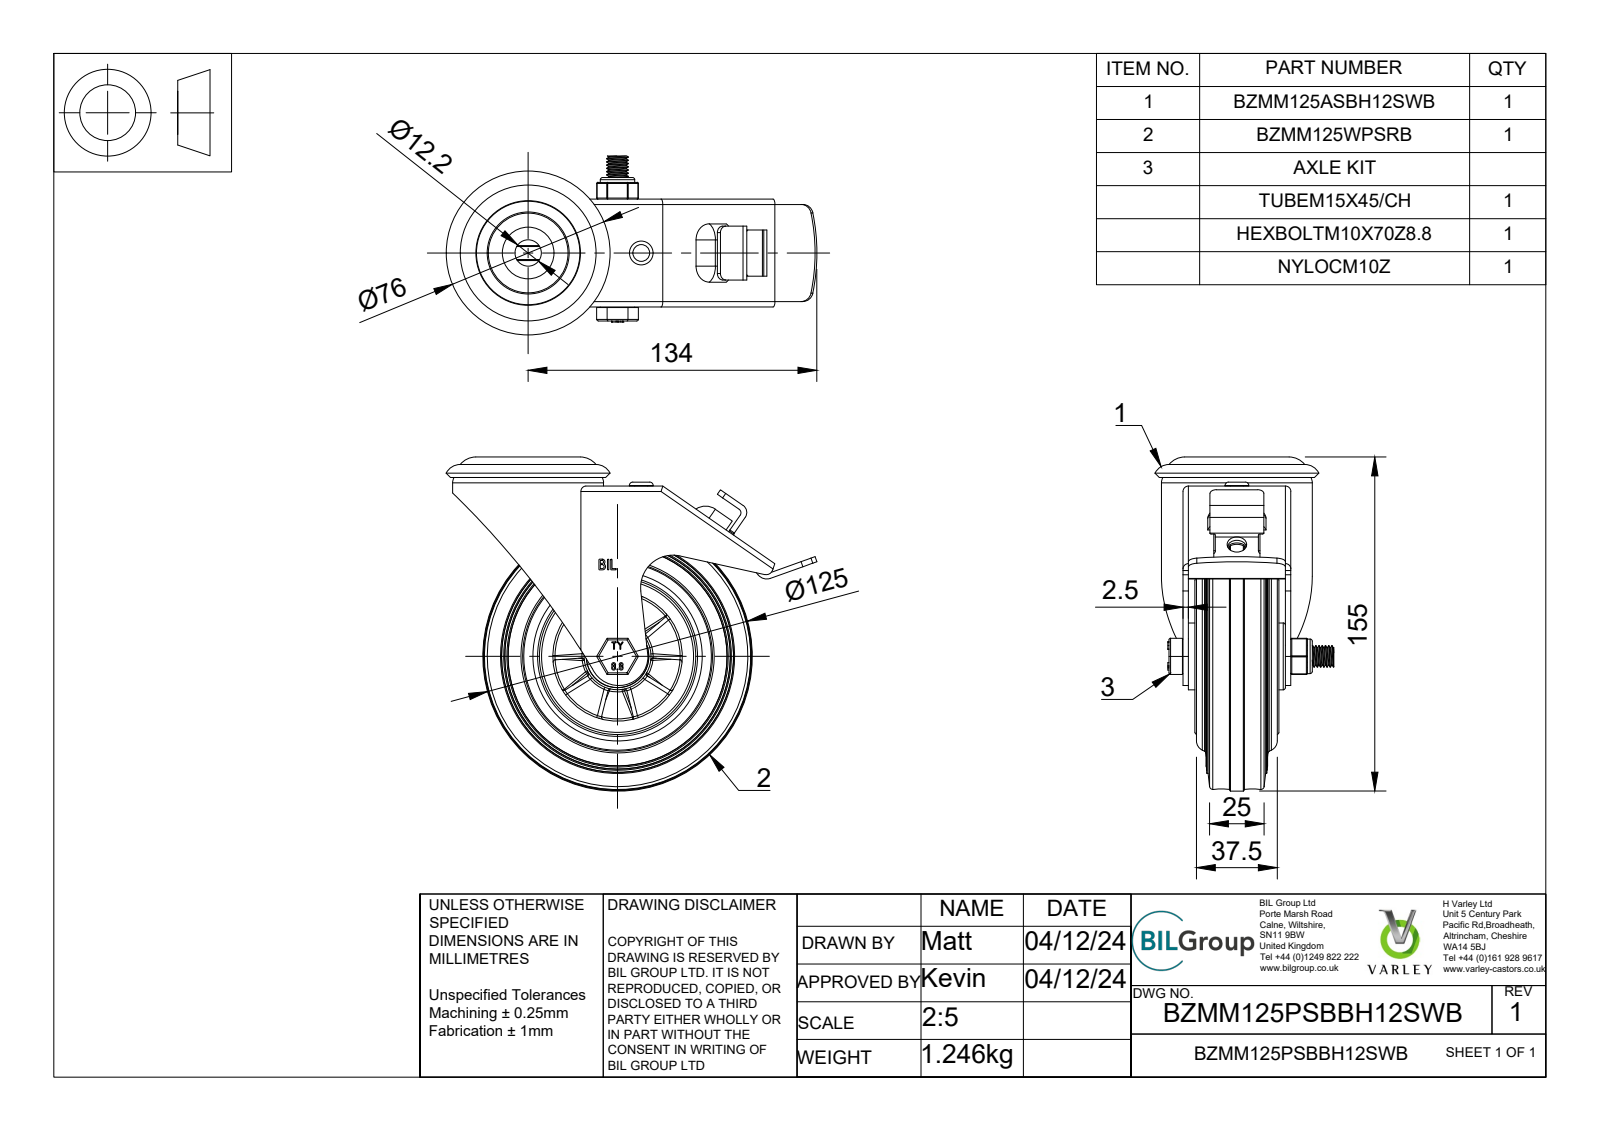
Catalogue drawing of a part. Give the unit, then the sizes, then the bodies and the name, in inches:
Units: inches
Overall size (bounding box): 6.772 × 6.102 × 3.268
Round holes (diameter × count): ⌀0.236 ×2, ⌀0.354 ×1, ⌀0.394 ×1, ⌀0.402 ×1, ⌀0.472 ×1, ⌀0.48 ×1, ⌀0.591 ×1, ⌀0.598 ×1, ⌀0.896 ×1, ⌀1.142 ×1, ⌀2.362 ×1, ⌀2.559 ×1
Round bosses / shafts (diameter × count): ⌀0.157 ×8, ⌀4.921 ×1, ⌀2.756 ×1, ⌀1.949 ×1, ⌀1.496 ×1, ⌀1.22 ×1, ⌀1.138 ×1, ⌀0.945 ×1
Partial cylindrical surfaces — rounded edges, fillets, slot ends (radius × count): R0.03 ×54, R0.02 ×32, R0.049 ×6, R0.118 ×6, R0.157 ×6, R0.098 ×5, R0.079 ×3, R0.197 ×3
Main face-to-face distances: 0.098, 1.87, 1.772, 0.256, 1.969, 0.197, 0.118, 0.039, 0.079, 0.217
Hole centre spacings: 2.067
Volume: 25.4 in³ · Surface area: 257.7 in²
Bodies: 22 solids, 1024 faces (384 planar, 243 cylindrical, 397 other)
Part name (STEP PRODUCT): BZMM125PSBBH12SWB v3; BZMM125ASBH12SWB v1; ZINC PLATED, PRESSED STEEL HEAD; ZINC PLATED, PRESSED STEEL FORKS (+8 more)
STEP written by: Autodesk Translation Framework v13.20.0.188 (AP242_MANAGED_MODEL_BASED_3D_ENGINEERING_MIM_LF)
